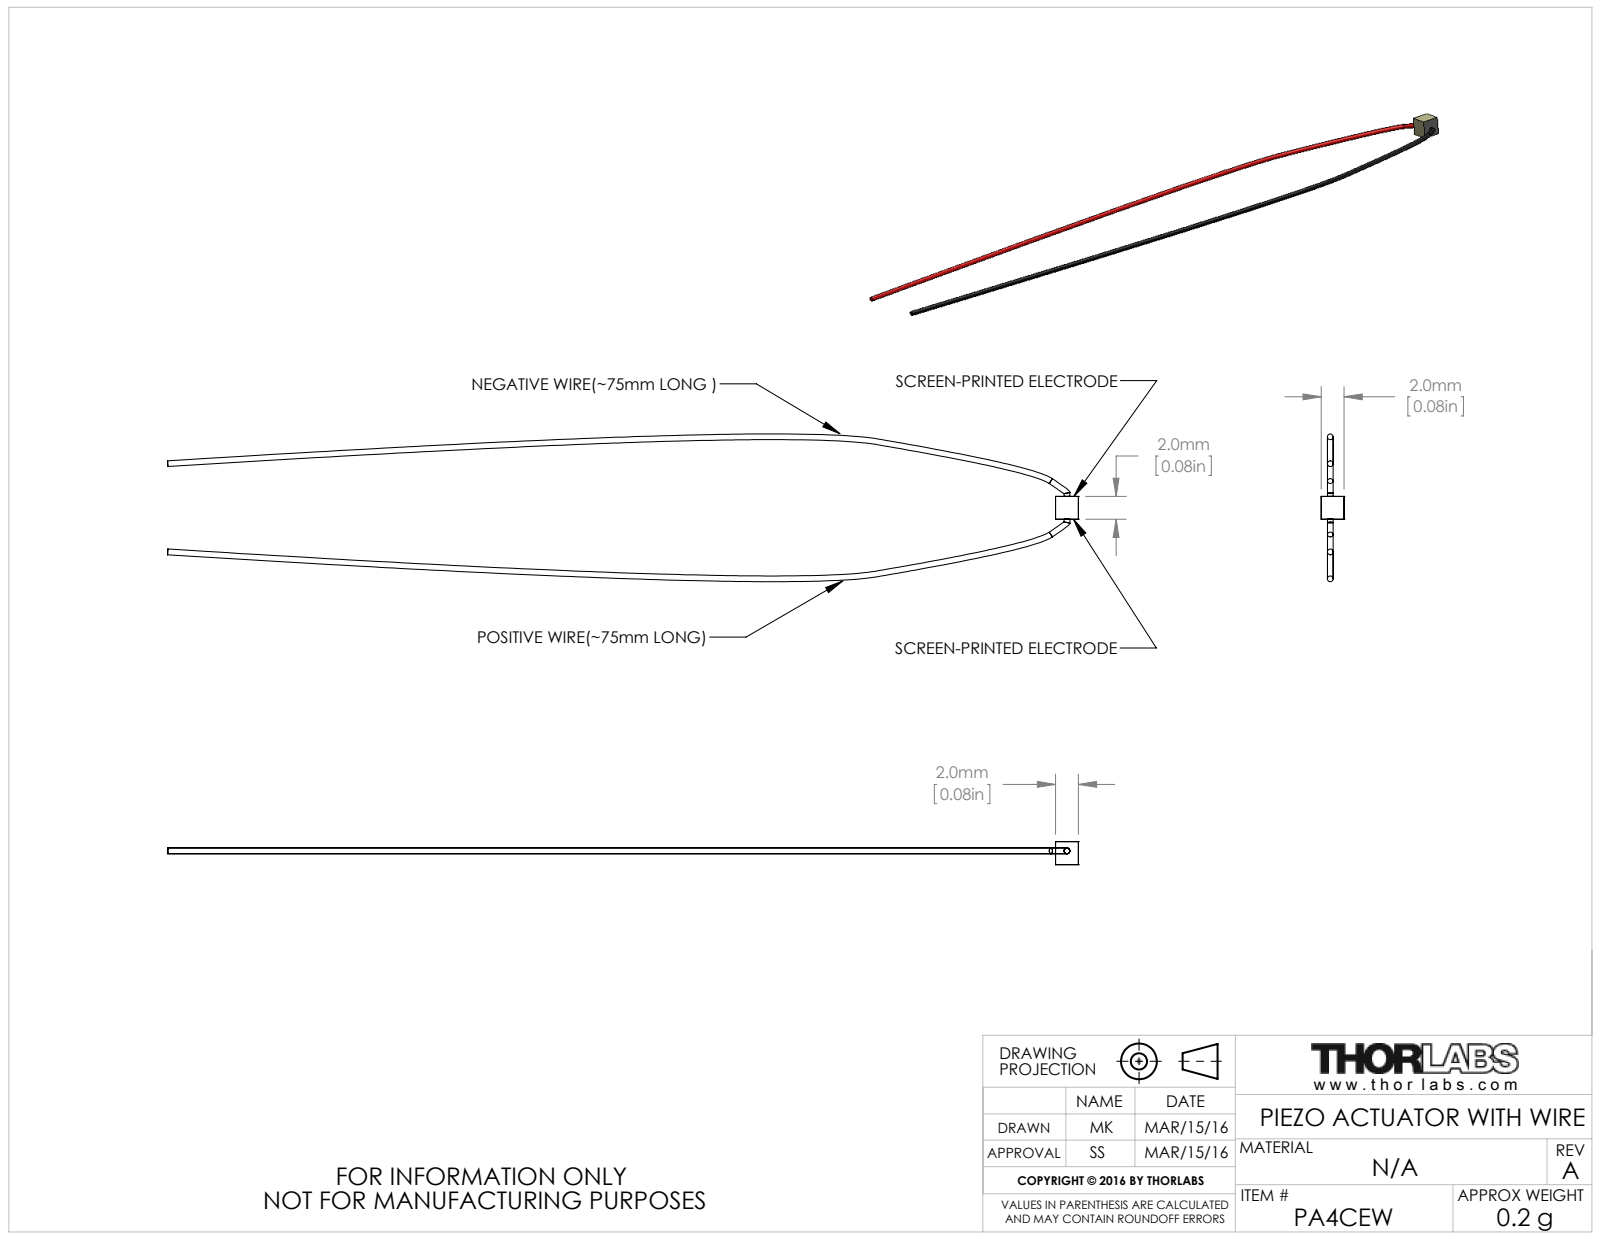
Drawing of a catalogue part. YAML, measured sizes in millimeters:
part_name: "CTN002580"
step_written_by: "SolidWorks 2014 (AUTOMOTIVE_DESIGN)"
units: millimeters
bodies: {solids: 1, faces: 20, planar: 8, cylindrical: 4, other: 8}
overall_size: [79.53, 12.9, 2]
volume: 39
surface_area: 274
round_bosses_or_shafts:
  - {diameter: 0.5, count: 1}
face_to_face_distances: [2]
